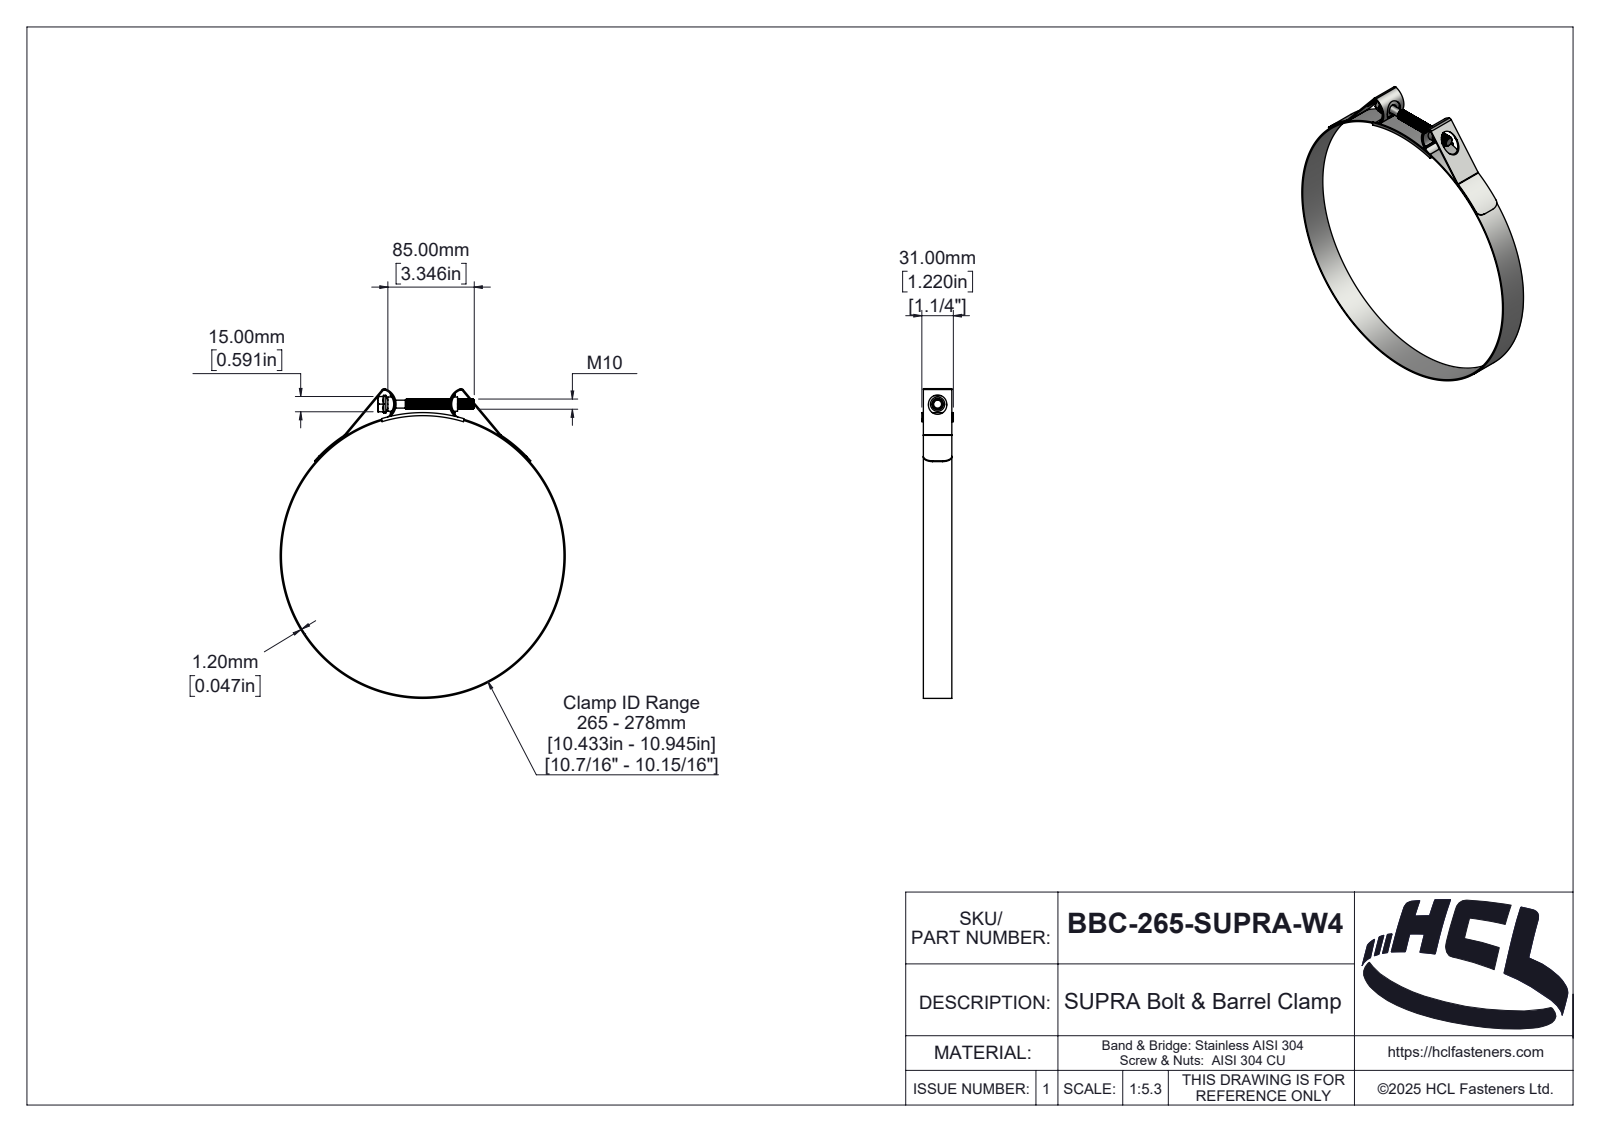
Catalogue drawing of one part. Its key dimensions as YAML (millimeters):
part_name: "BBC-265-SUPRA-W4"
step_written_by: "SolidWorks 2025 (AUTOMOTIVE_DESIGN)"
units: millimeters
bodies: {solids: 5, faces: 380, planar: 50, cylindrical: 244, other: 86}
overall_size: [304.56, 280.4, 31]
volume: 47298
surface_area: 74206
round_holes:
  - {diameter: 278, count: 1}
round_bosses_or_shafts:
  - {diameter: 280.4, count: 1}
  - {diameter: 17.32, count: 1}
  - {diameter: 14, count: 1}
  - {diameter: 10, count: 1}
  - {diameter: 7.8, count: 1}
partial_cylinders:
  - {radius: 1, count: 4}
  - {radius: 1.3, count: 2}
  - {radius: 2, count: 2}
  - {radius: 2.5, count: 2}
  - {radius: 3.2, count: 2}
  - {radius: 9, count: 2}
  - {radius: 13.66, count: 2}
  - {radius: 14.66, count: 2}
face_to_face_distances: [1.2, 28, 1.5, 29.5, 29.8, 28.3, 31, 28.6, 15, 2.5]
